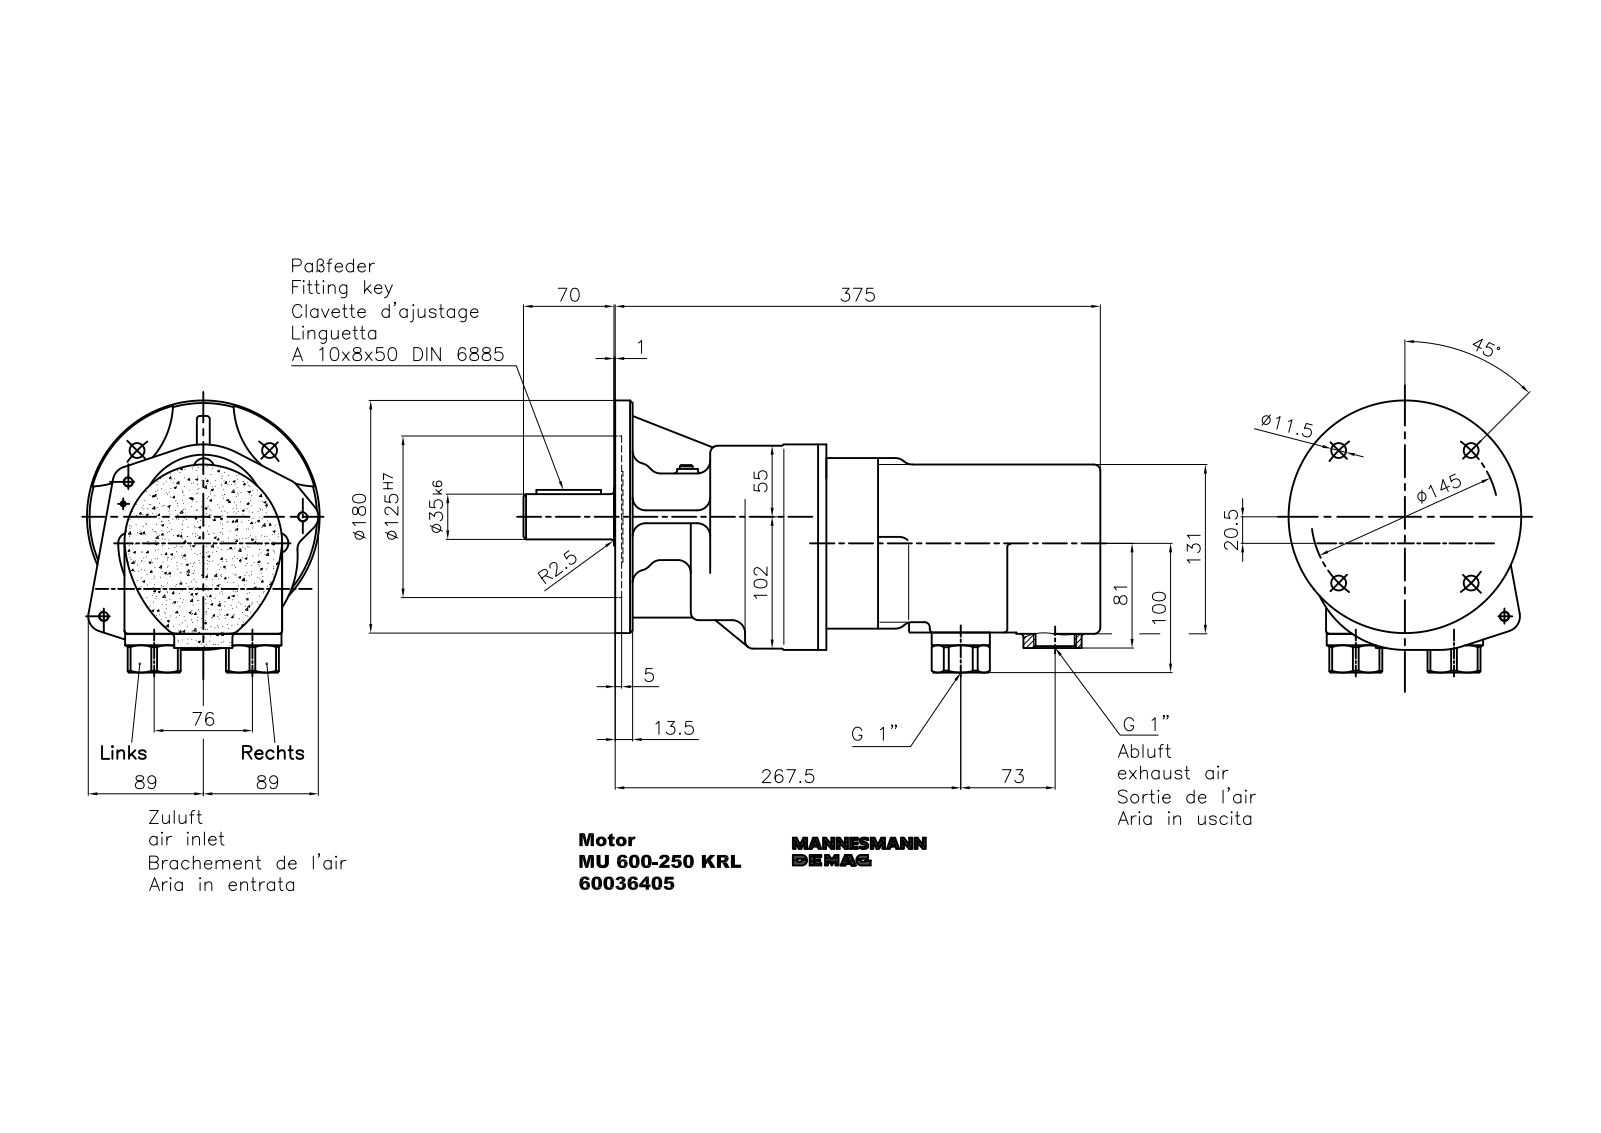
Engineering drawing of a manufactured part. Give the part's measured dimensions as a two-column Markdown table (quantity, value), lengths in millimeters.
| quantity | value |
| --- | --- |
| part name | MU 600-250 KRL_60036405 |
| STEP written by | Autodesk Inventor 2018 (AUTOMOTIVE_DESIGN) |
| units | millimeters |
| bodies | 2 solids, 1030 faces (363 planar, 365 cylindrical, 302 other) |
| overall size | 446.7 × 205.58 × 180 |
| volume | 4 791 000 mm³ |
| surface area | 387 677 mm² |
| round holes (diameter × count) | 4.92 × 8, 9.5 × 6, 6 × 4, 6.65 × 4, 7 × 4, 11.5 × 4, 8.5 × 3, 30.29 × 3, 5 × 2, 6.5 × 2, 18 × 2, 24.12 × 2 |
| round bosses / shafts (diameter × count) | 14.8 × 3, 13 × 3, 8 × 3, 41 × 2, 24.4 × 2, 180 × 1, 122 × 1, 115.48 × 1 |
| partial cylindrical surfaces (radius × count) | 2.5 × 32, 2 × 30, 4 × 20, 10 × 14, 6 × 12, 11 × 12, 5 × 11, 3 × 8 |
| main face-to-face distances | 5, 1, 375.9, 7.5, 370.9, 212, 158.9, 163.9, 8.5, 362.4 |
| hole center spacings | 30, 54, 72.51, 81.71, 82.02, 102.54, 130.83, 139.36 |
